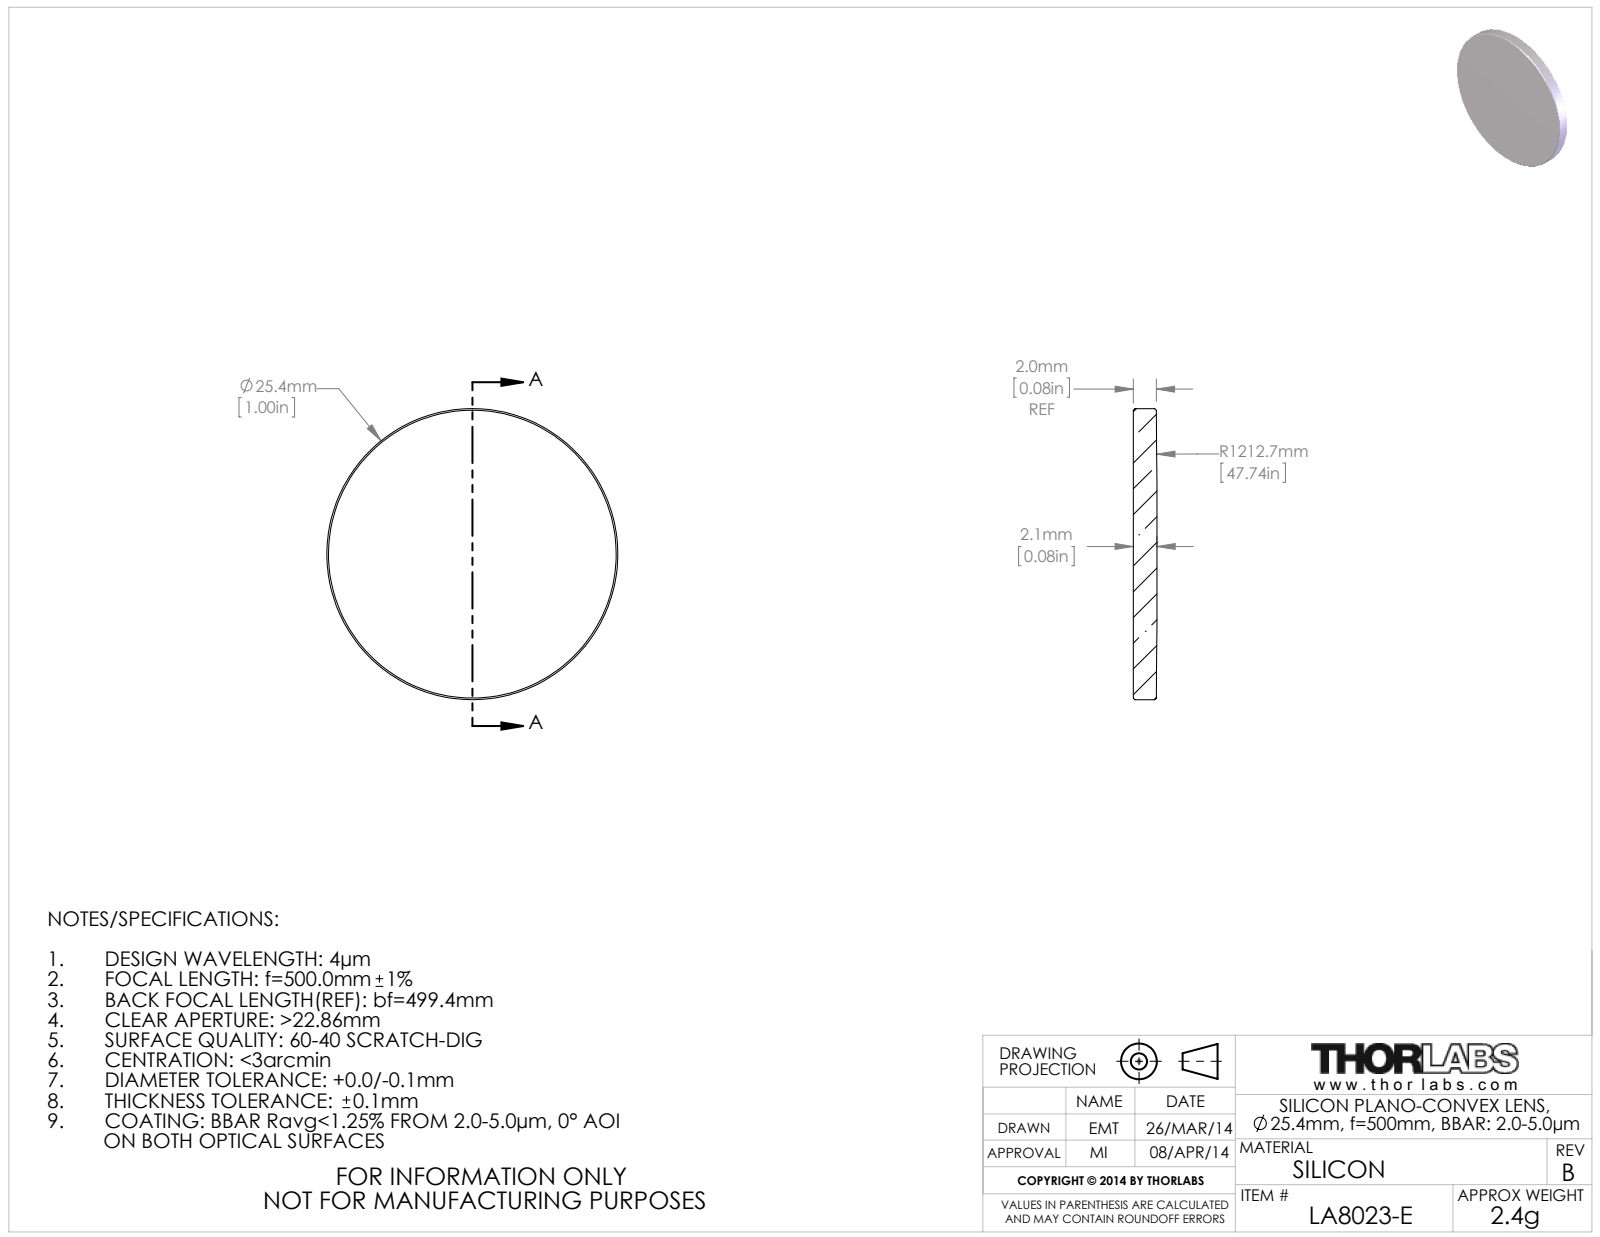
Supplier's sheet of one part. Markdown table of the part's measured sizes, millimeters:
| quantity | value |
| --- | --- |
| part name | 20122-E0W |
| STEP written by | SolidWorks 2014 (CONFIG_CONTROL_DESIGN) |
| units | millimeters |
| bodies | 1 solid, 9 faces (1 planar, 2 cylindrical, 6 other) |
| overall size | 25.4 × 25.4 × 2.07 |
| volume | 1 030 mm³ |
| surface area | 1 160 mm² |
| round bosses / shafts (diameter × count) | 25.4 × 1 |
